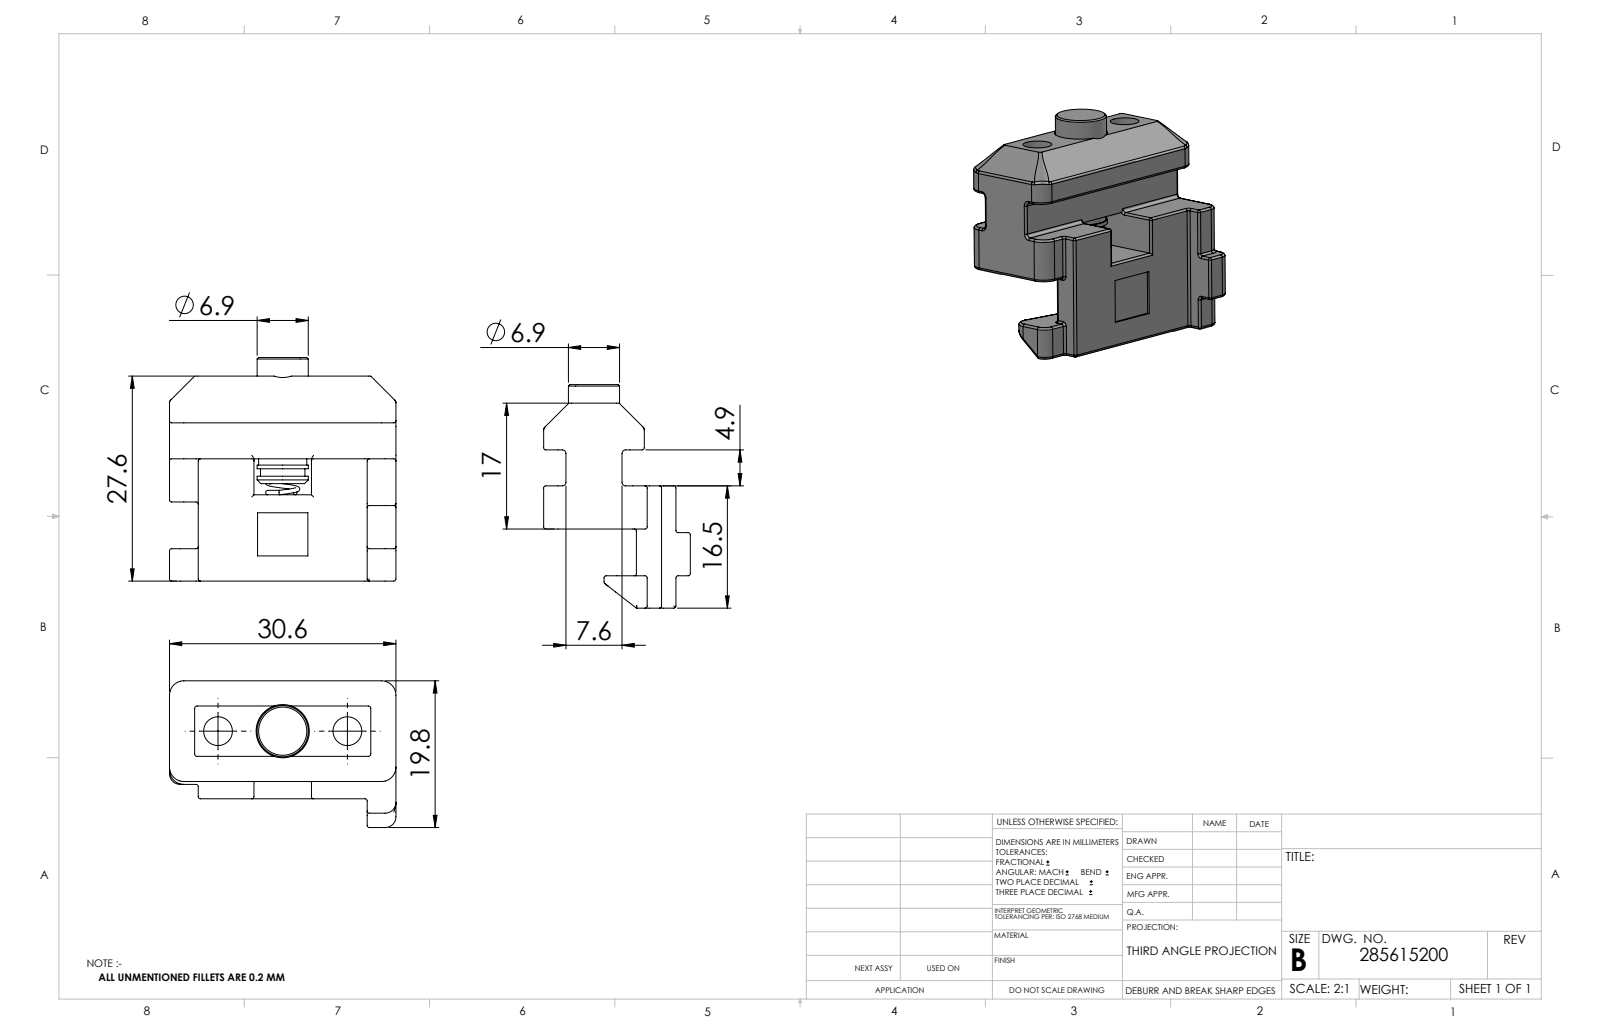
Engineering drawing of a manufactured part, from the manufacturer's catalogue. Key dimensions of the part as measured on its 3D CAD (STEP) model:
Part name (STEP PRODUCT): 285615200
STEP written by: SolidWorks 2014 (AUTOMOTIVE_DESIGN)
Units: millimetres
Bodies: 6 solids, 503 faces (112 planar, 221 cylindrical, 170 other)
Overall size (bounding box): 52.41 × 31.69 × 31.17
Volume: 13 451 mm³ · Surface area: 10 273 mm²
Round holes (diameter × count): ⌀3.88 ×2, ⌀4.02 ×2, ⌀5 ×2, ⌀7.18 ×1, ⌀7.44 ×1
Round bosses / shafts (diameter × count): ⌀6.9 ×2, ⌀6.5 ×2, ⌀6 ×2
Partial cylindrical surfaces — rounded edges, fillets, slot ends (radius × count): R0.29 ×61, R0.3 ×61, R0.48 ×8, R0.5 ×8, R1.94 ×6, R2.01 ×6, R1.46 ×3, R1.51 ×3
Main face-to-face distances: 0.63, 20, 5.03, 17.6, 4.85, 0.42, 10.67, 6.54, 16.97, 6.03
Hole centre spacings: 8.73, 38.58, 9.05, 9.06, 17.46, 18.11, 38.59, 39.43
